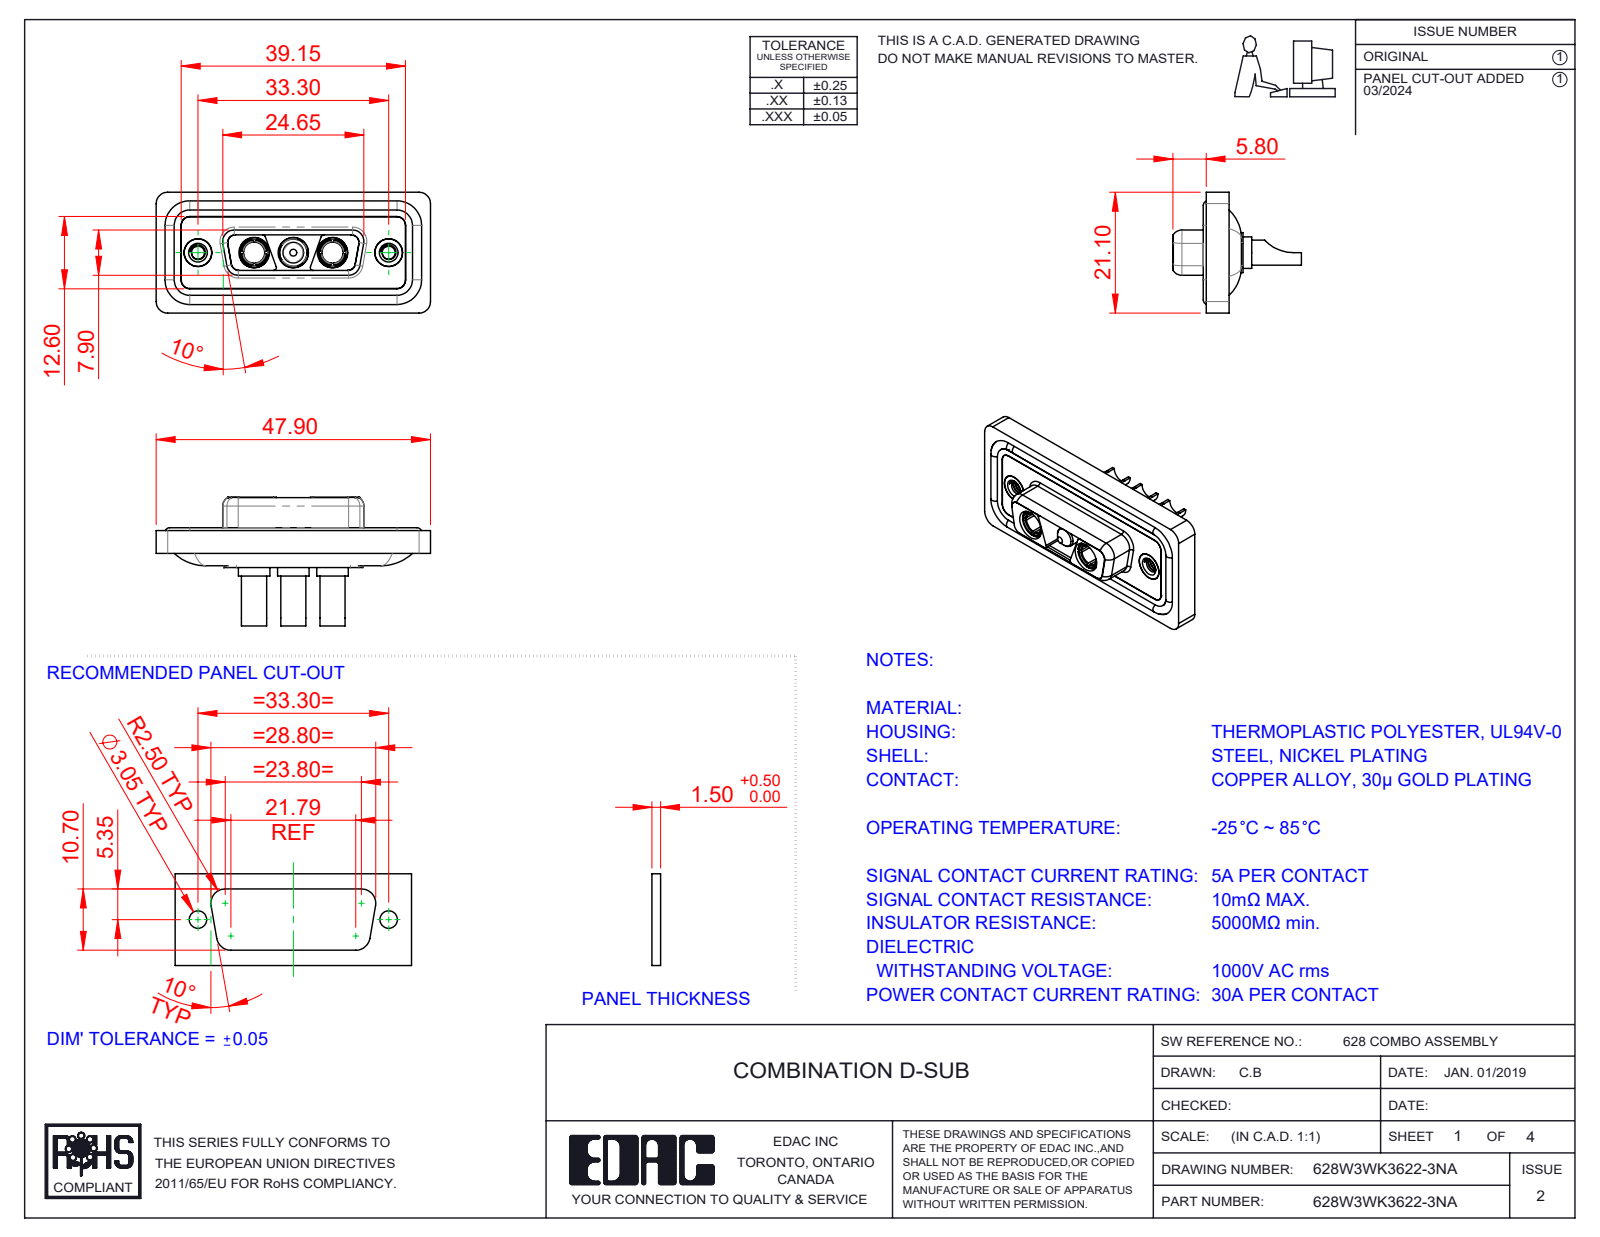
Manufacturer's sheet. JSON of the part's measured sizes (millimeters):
{"part_name": "628W3WK3622-3NA; 628Combo Housing_3WK3; 628Combo Threaded Rivet_A; 628Combo Shell Rear_15 Contacts (+4 more)", "step_written_by": "SolidWorks 2023 (CONFIG_CONTROL_DESIGN)", "units": "millimeters", "bodies": {"solids": 13, "faces": 599, "planar": 187, "cylindrical": 269, "other": 143}, "overall_size": [47.9, 22.45, 21.1], "volume_mm3": 5952, "surface_area_mm2": 9825, "round_holes": [[4.85, 5], [3.5, 3], [5.3, 3], [2.26, 2], [3.7, 2], [4, 2], [4.05, 2], [5, 2]], "round_bosses_or_shafts": [[1.6, 4], [5.5, 3], [5.2, 3], [4.75, 3], [4.4, 3], [3.75, 3], [4.96, 2], [4.95, 2]], "partial_cylinders_radius": [[1.5, 22], [2, 20], [1.35, 12], [0.5, 8], [1.6, 8], [0.25, 4], [0.6, 4], [0.65, 4]], "face_to_face_distances": [0.4, 1.6, 0.5, 1.1, 2.9, 1.8, 5.65, 7.05, 5.35, 6.6], "hole_center_spacings": [6.85, 9.8, 16.65, 23.5, 13.7, 33.3]}
